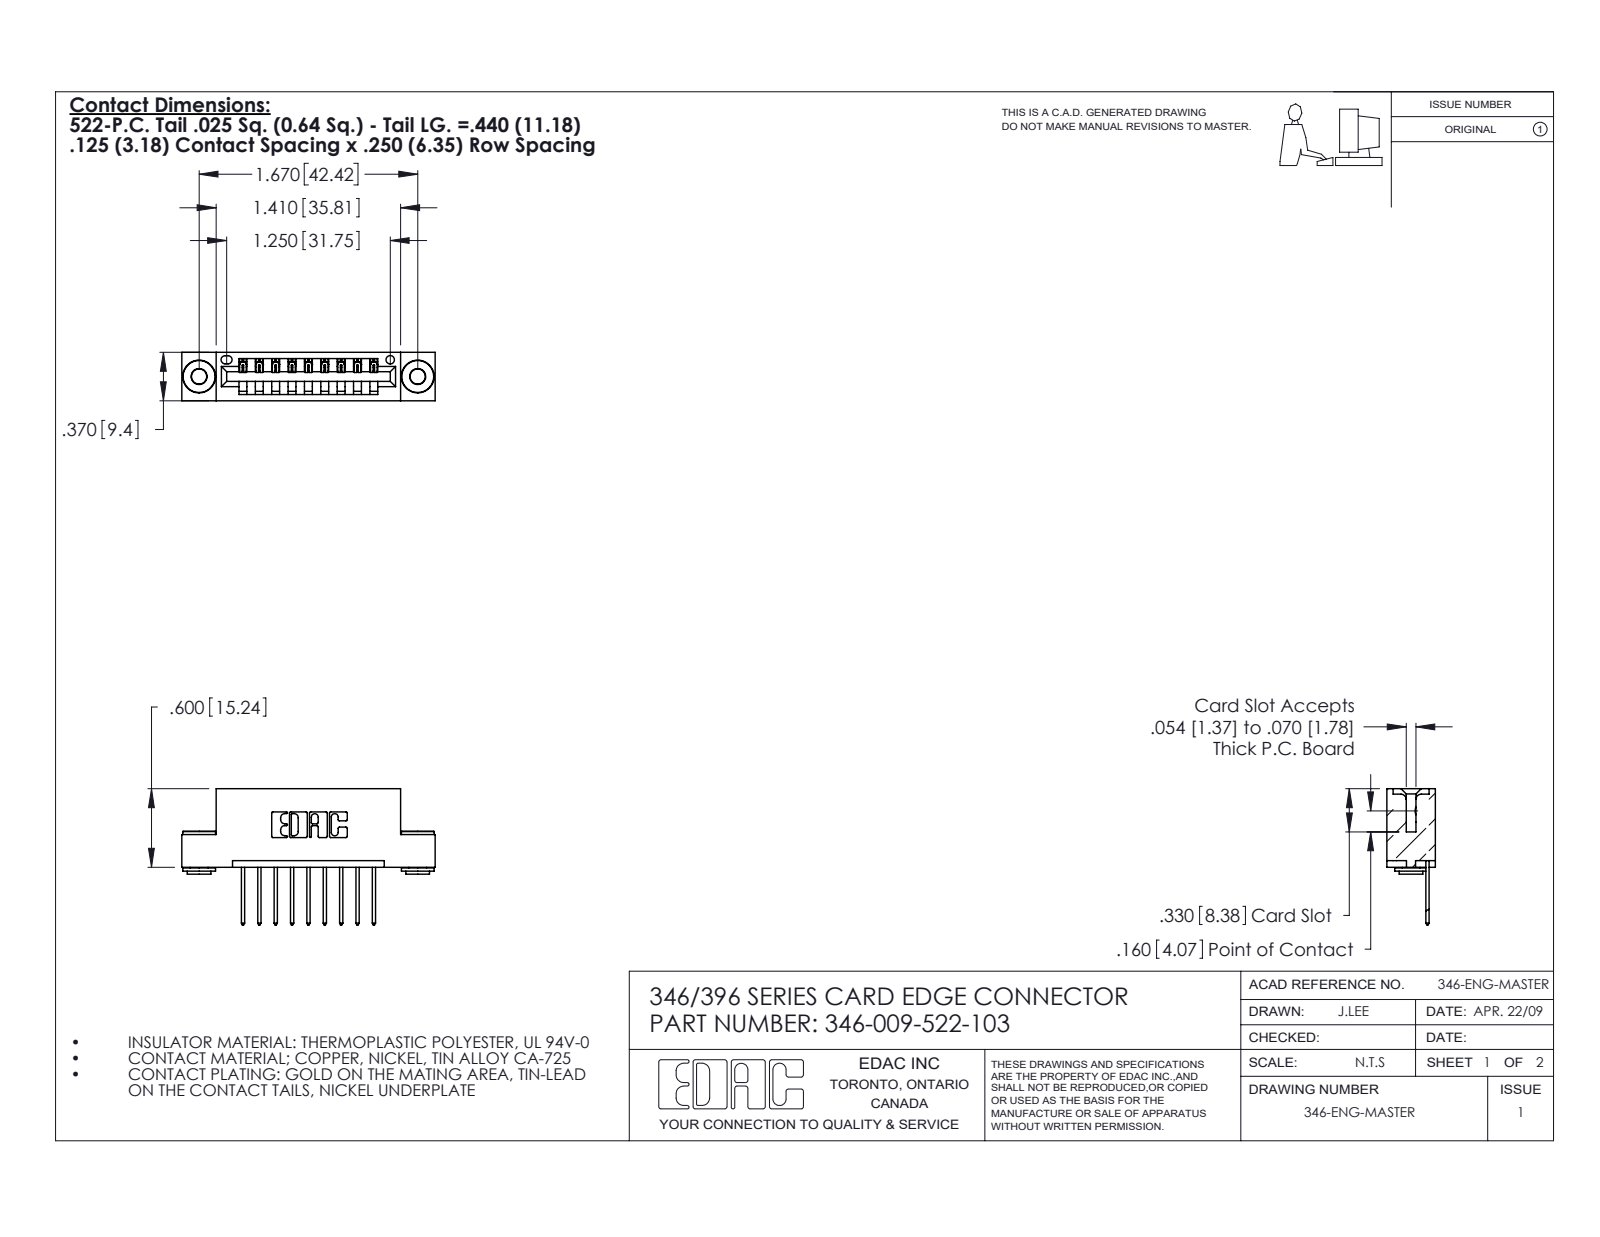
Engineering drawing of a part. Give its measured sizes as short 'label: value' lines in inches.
name: 346 Part_Flush Mounting Lugs - 0.156 Dia-TH; 345-292-001_345-293-122; 346-009-522-103; 345-250-002_345-250-002-102
written by: SolidWorks 2020 (CONFIG_CONTROL_DESIGN)
unit: in
bodies: 12 solids, 696 faces (460 planar, 228 cylindrical, 8 other)
size: 1.935 × 1.04 × 0.37
volume: 0.273 in³; area: 8.568 in²
holes: 2× ⌀0.116, 2× ⌀0.156, 1× ⌀0.064
bosses: 2× ⌀0.25, 2× ⌀0.18, 2× ⌀0.136
rounds: 22× R0.01, 18× R0.006, 18× R0.01, 6× R0.007, 6× R0.031, 3× R0.026, 2× R0.031, 2× R0.04
face distances: 0.25, 0.048, 0.322, 0.37, 0.025, 0.072, 0.298, 0.148, 0.222, 0.1
hole spacings: 0.246, 1.465, 1.67
